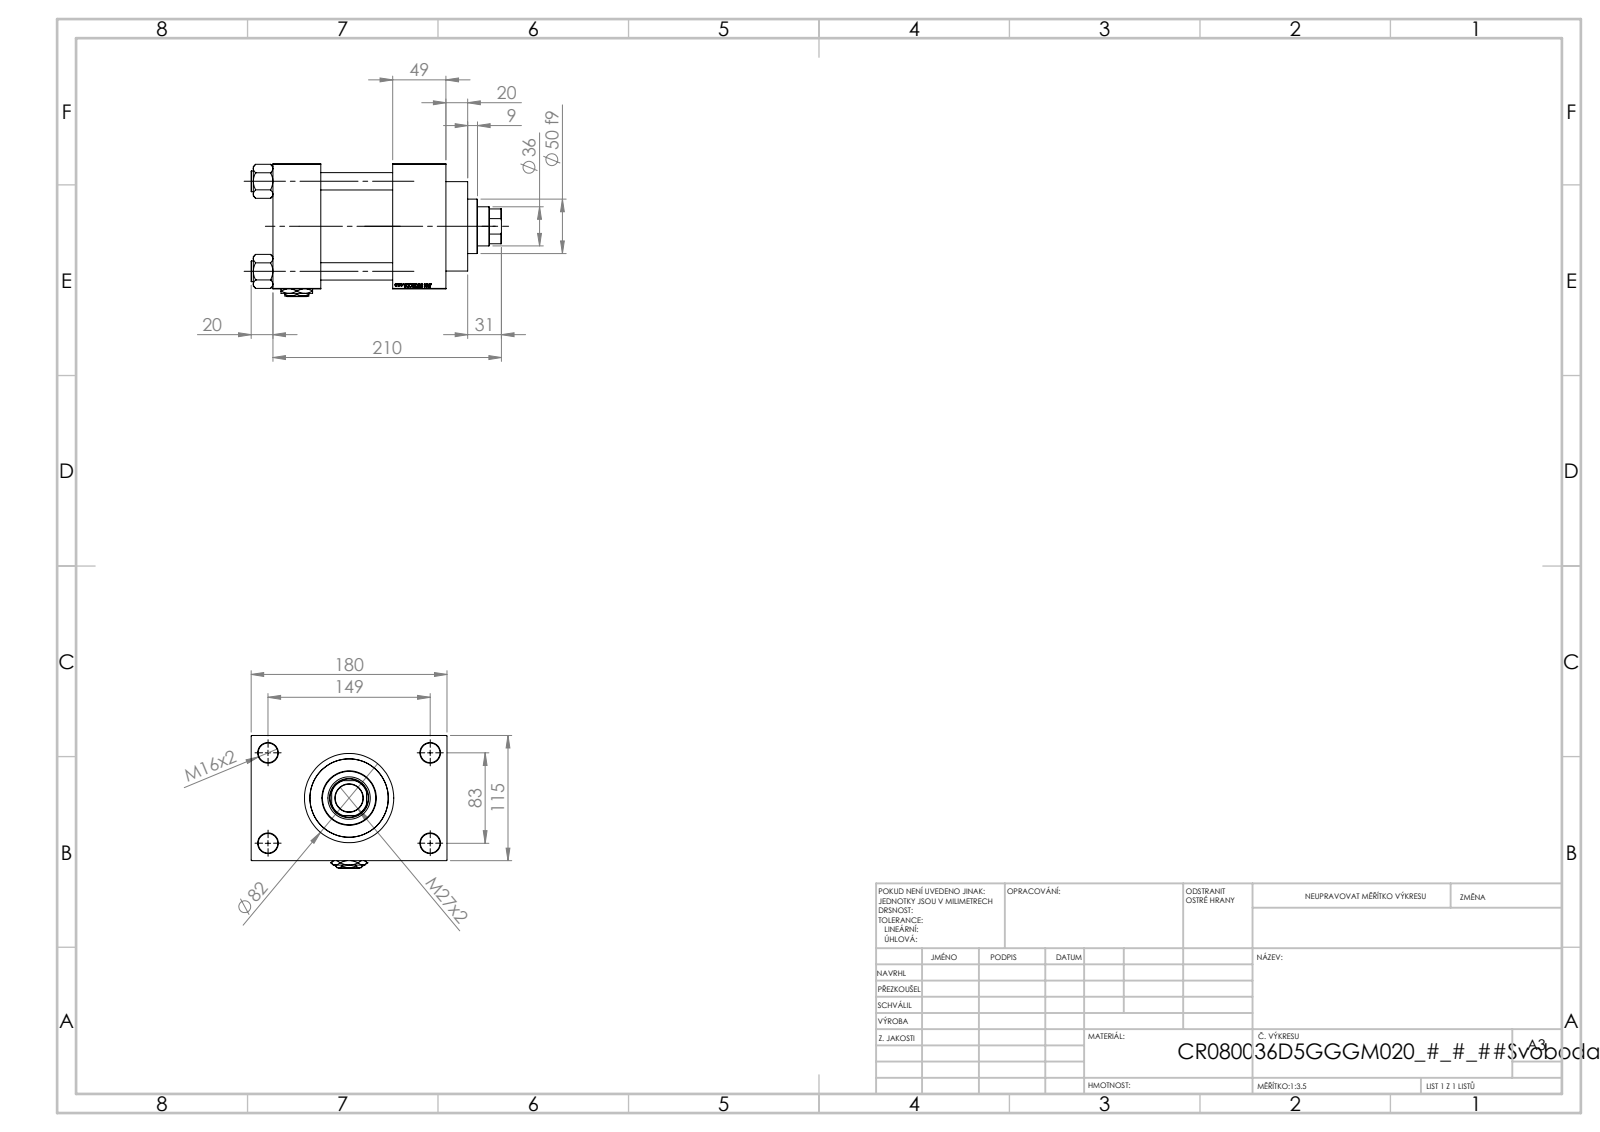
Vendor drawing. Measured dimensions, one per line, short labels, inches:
name: V215CR_VCP_D; NUT_M5_D; V215_VC_A; V215CR_D_TYCINKA (+2 more)
written by: SolidWorks 2019 (CONFIG_CONTROL_DESIGN)
unit: in
bodies: 12 solids, 1205 faces (569 planar, 96 cylindrical, 540 other)
size: 9.055 × 7.087 × 4.803
volume: 121.6 in³; area: 461.4 in²
holes: 4× ⌀0.63, 4× ⌀0.709, 2× ⌀0.276, 2× ⌀1.041, 2× ⌀1.378, 1× ⌀1.004, 1× ⌀1.417, 1× ⌀1.535, 1× ⌀2.402, 1× ⌀2.835, 1× ⌀3.15
bosses: 4× ⌀0.748, 1× ⌀3.386, 1× ⌀3.228, 1× ⌀1.969
rounds: 1× R0.689
face distances: 4.528, 2.598, 4.331, 1.929, 1.732, 6.26, 1.28, 5.807, 0.787, 2.717
hole spacings: 1.305, 2.302, 3.256, 3.357, 3.513, 4.561, 5.607, 3.268
